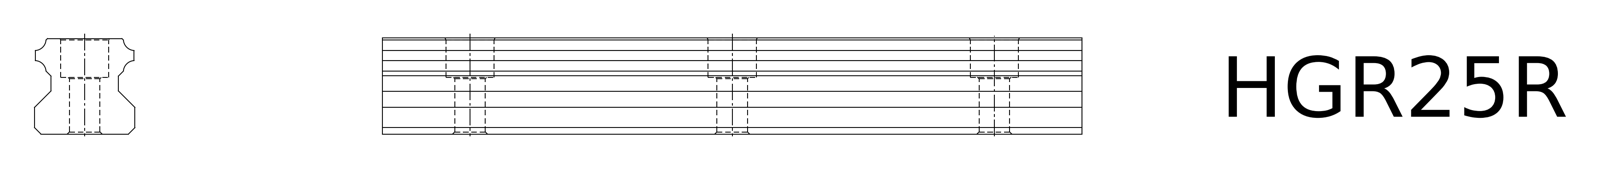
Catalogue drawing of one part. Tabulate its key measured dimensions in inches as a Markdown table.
| quantity | value |
| --- | --- |
| part name | HGR25R |
| STEP written by | SolidWorks 2006104 (CONFIG_CONTROL_DESIGN) |
| units | inches |
| bodies | 1 solid, 59 faces (25 planar, 34 cylindrical, 0 other) |
| overall size | 5.906 × 0.906 × 0.866 |
| volume | 3.765 in³ |
| surface area | 24.93 in² |
| round holes (diameter × count) | 0.276 × 3, 0.433 × 3 |
| partial cylindrical surfaces (radius × count) | 0.02 × 12, 0.039 × 6, 0.096 × 4 |
| main face-to-face distances | 0.866, 0.906, 0.142, 0.764, 0.772, 5.906, 0.622, 0.433, 0.339, 1.124 |
| hole center spacings | 2.362, 4.724 |
